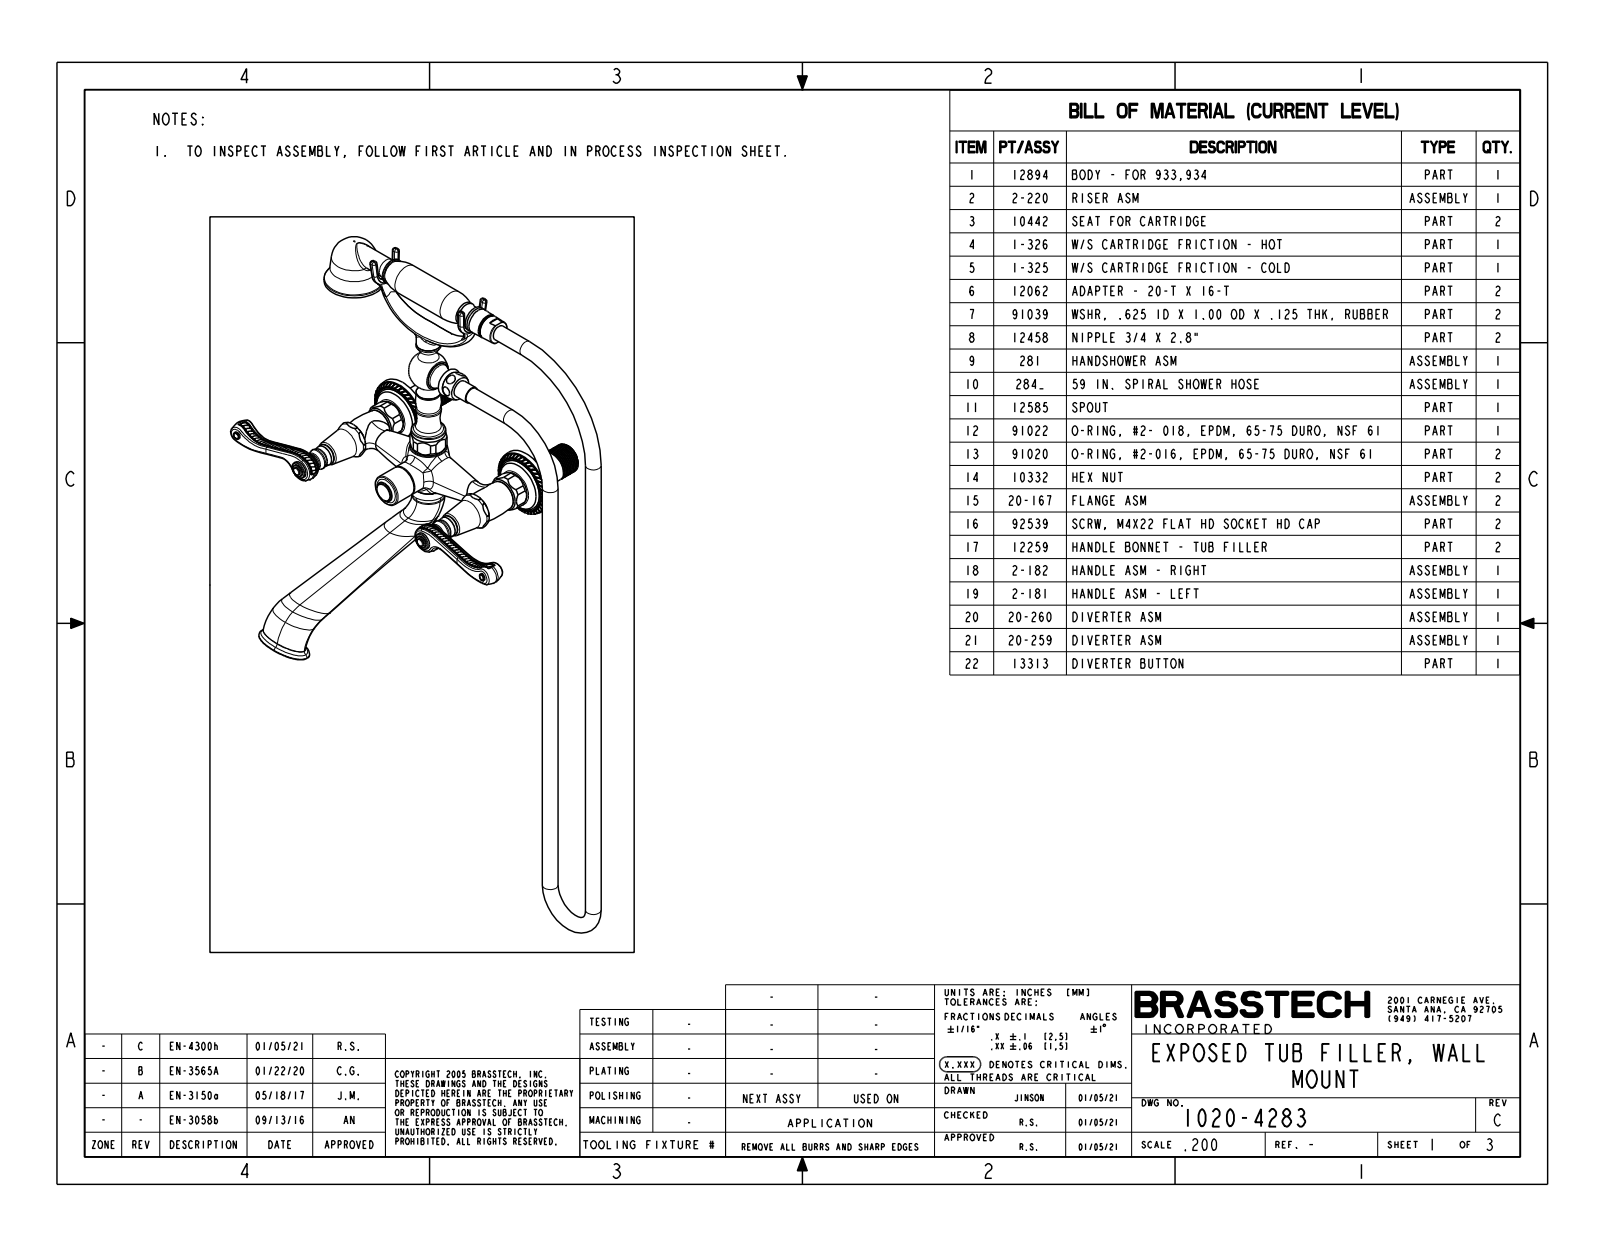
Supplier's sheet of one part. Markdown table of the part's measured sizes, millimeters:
| quantity | value |
| --- | --- |
| part name | 1020-4283 |
| STEP written by | CREO PARAMETRIC BY PTC INC, 2018400 (CONFIG_CONTROL_DESIGN) |
| units | millimeters |
| bodies | 1 solid, 1733 faces (330 planar, 421 cylindrical, 982 other) |
| overall size | 606 × 371.4 × 234.5 |
| volume | 830 000 mm³ |
| surface area | 174 400 mm² |
| round holes (diameter × count) | 1.2 × 52 |
| round bosses / shafts (diameter × count) | 20.8 × 4, 13.7 × 4, 6.6 × 4, 15.2 × 3, 47.1 × 2, 18.5 × 2, 17.8 × 2, 11.2 × 2 |
| partial cylindrical surfaces (radius × count) | 3 × 84, 3.8 × 84, 2.2 × 32, 279.4 × 4, 16.2 × 3, 15.1 × 2, 10.3 × 1, 10.3 × 1 |
| main face-to-face distances | 30.2, 76.2, 86.3, 20.8, 28.2, 126.9, 98.7, 106.4, 46, 20.3 |
| hole center spacings | 4.7, 9.3, 13.6, 20.7, 25.9, 4.7, 15.3, 17.4 |
